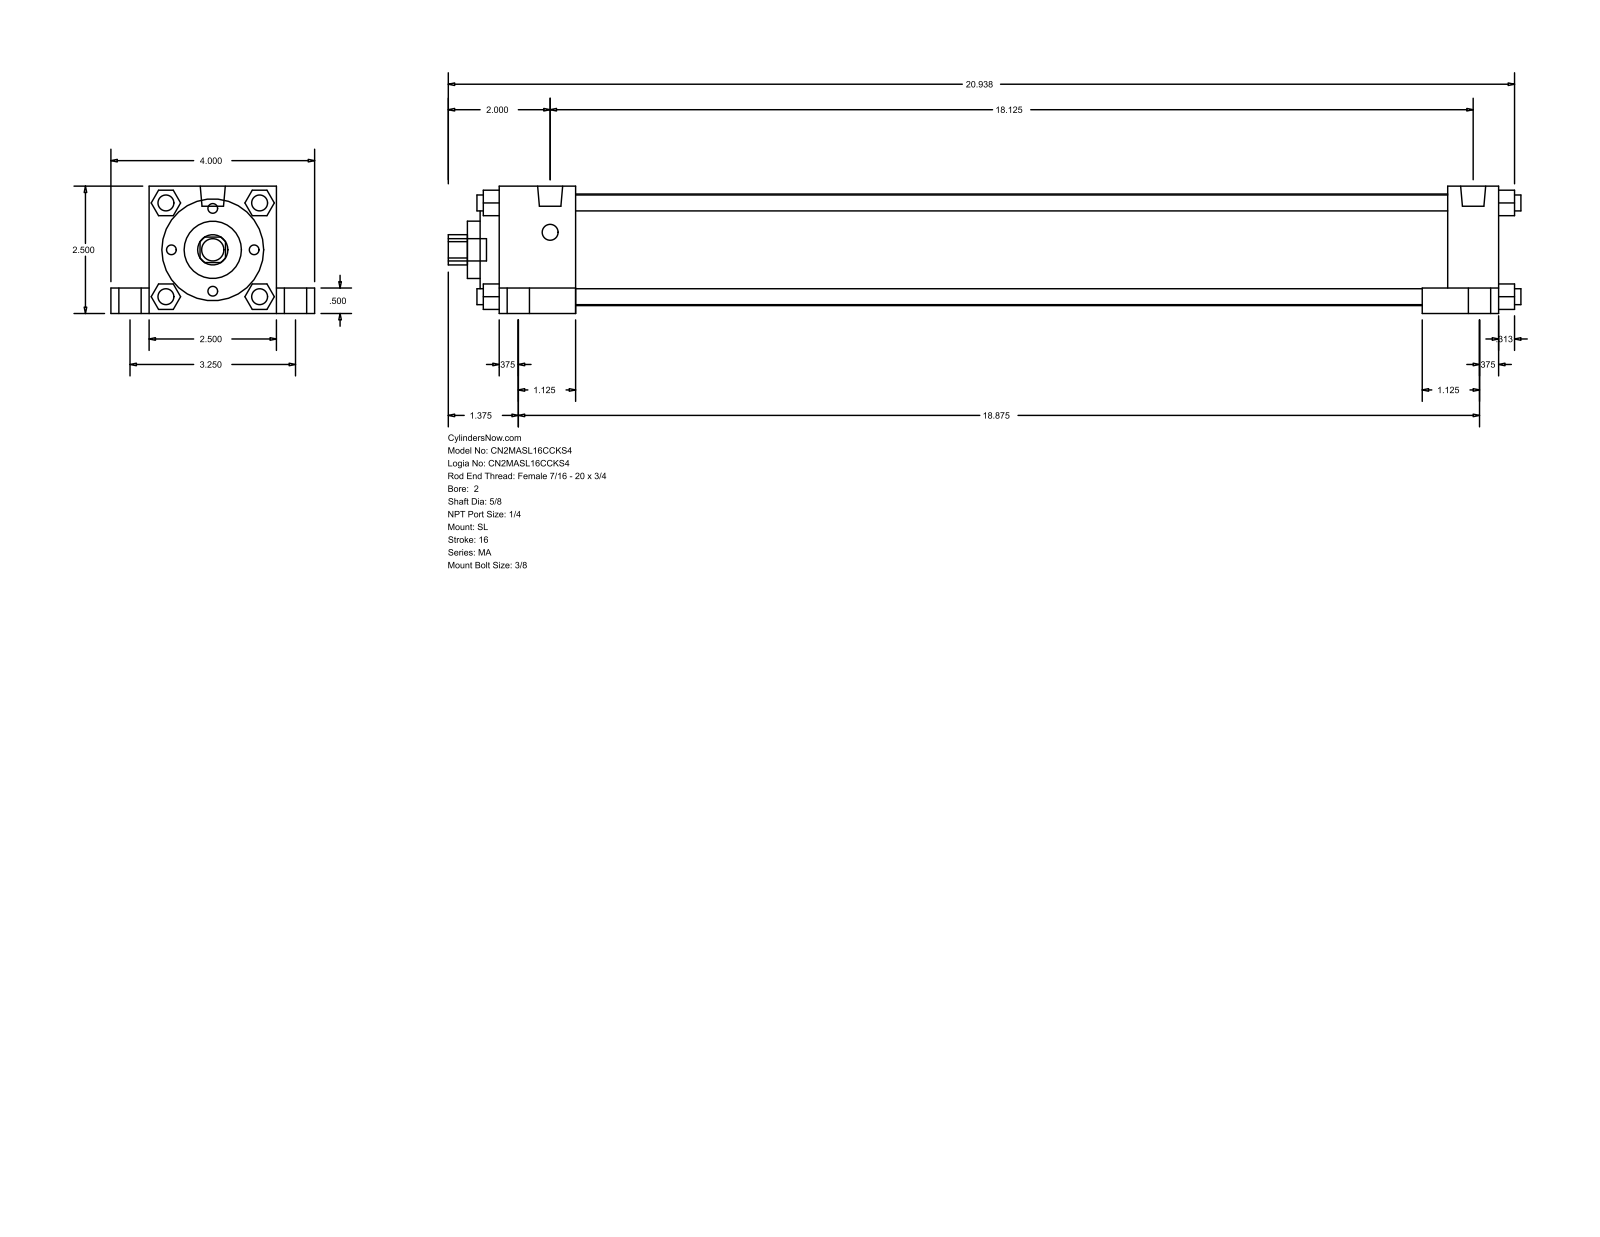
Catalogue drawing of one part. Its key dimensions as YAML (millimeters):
part_name: "MA_SL__0200_0.625"
step_written_by: "GSSL Pune (CONFIG_CONTROL_DESIGN)"
units: millimeters
bodies: {solids: 0, faces: 150, planar: 113, cylindrical: 37, other: 0}
overall_size: [534.99, 101.6, 63.5]
round_holes:
  - {diameter: 15.88, count: 1}
  - {diameter: 28.57, count: 1}
  - {diameter: 50.8, count: 1}
  - {diameter: 55.63, count: 1}
round_bosses_or_shafts:
  - {diameter: 7.94, count: 8}
  - {diameter: 11.11, count: 5}
  - {diameter: 17.46, count: 4}
  - {diameter: 12.49, count: 2}
partial_cylinders:
  - {radius: 7.54, count: 1}
face_to_face_distances: [63.5, 12.7, 9.52, 25.4, 19.05, 82.55, 38.1, 498.48, 50.8, 460.38]
